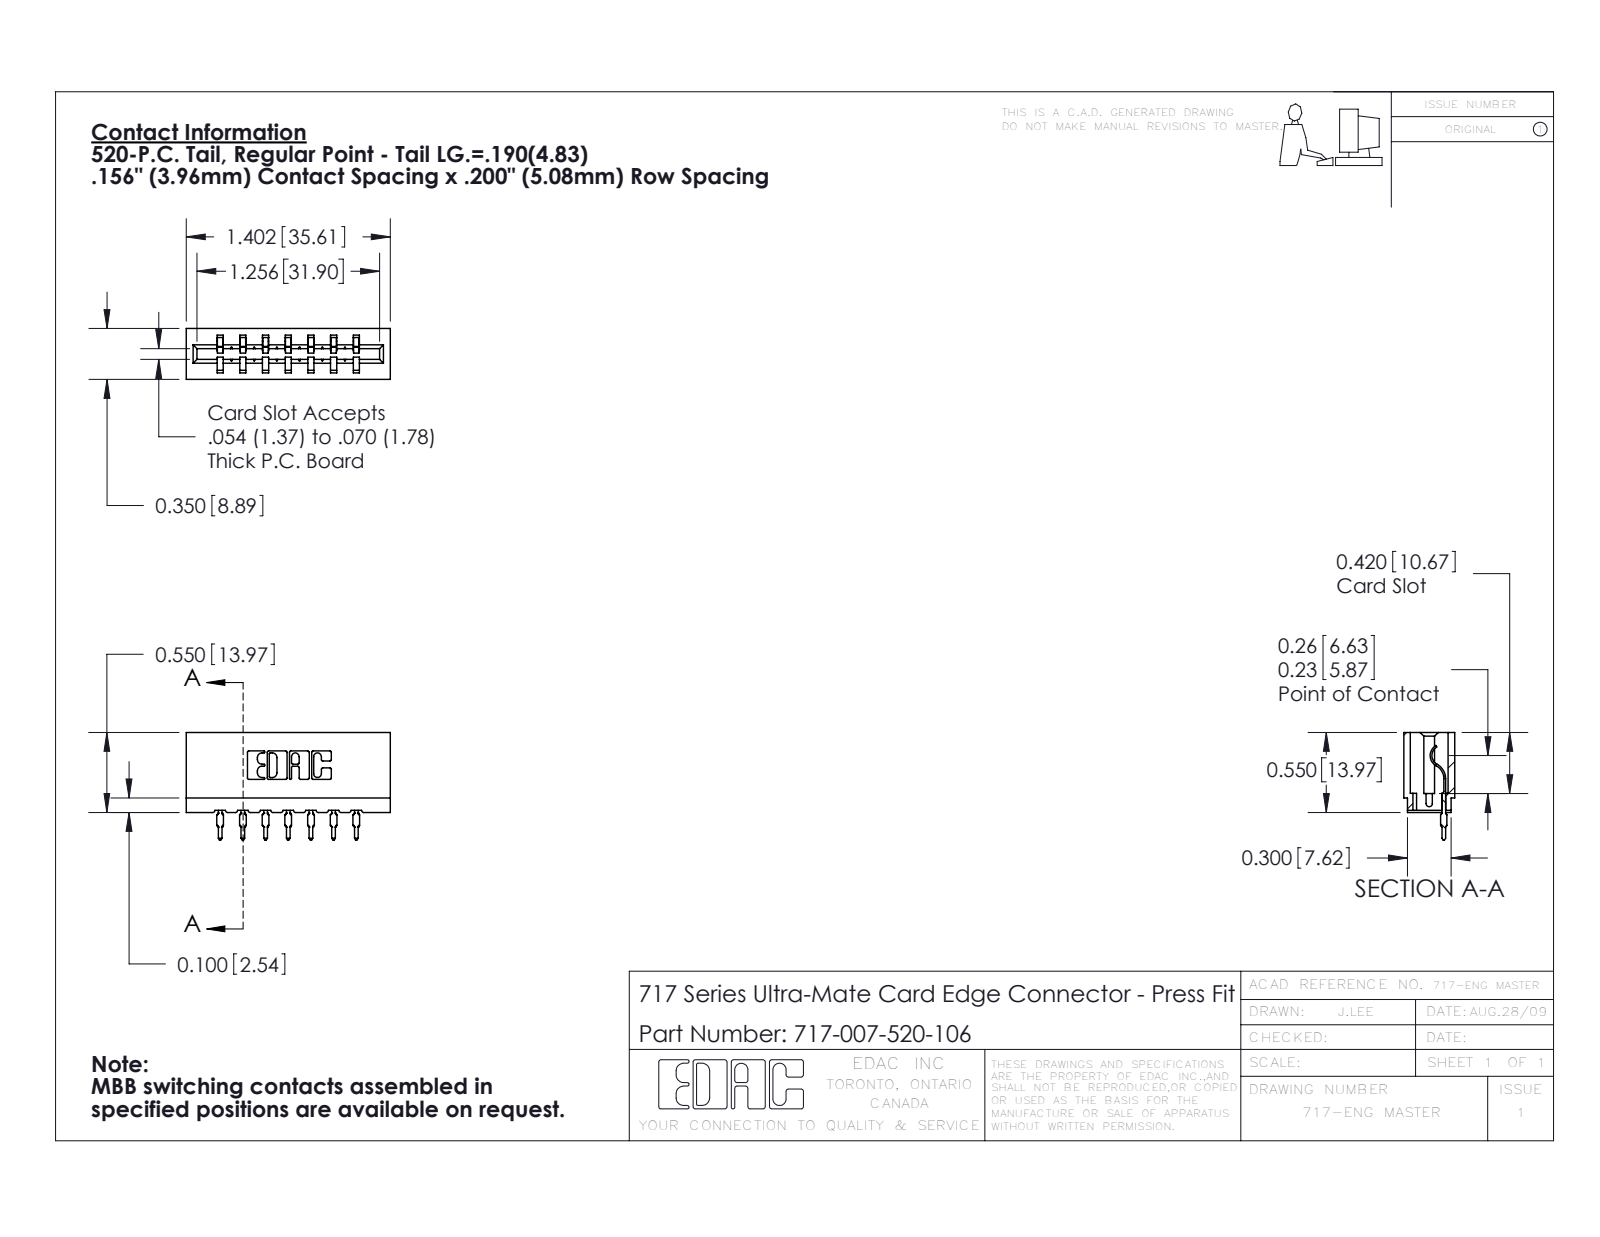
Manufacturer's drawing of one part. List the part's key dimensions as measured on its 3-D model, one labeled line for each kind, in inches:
Part name (STEP PRODUCT): 717-007-520-106; 745-292-001_520; 717 Part_Insulator Option - 06
STEP written by: SolidWorks 2016 (CONFIG_CONTROL_DESIGN)
Units: inches
Bodies: 8 solids, 885 faces (530 planar, 173 cylindrical, 182 other)
Overall size (bounding box): 1.402 × 0.739 × 0.35
Volume: 0.193 in³ · Surface area: 6.205 in²
Partial cylindrical surfaces — rounded edges, fillets, slot ends (radius × count): R0.01 ×22, R0.015 ×14, R0.021 ×14, R0.007 ×6, R0.031 ×6, R0.005 ×4, R0.011 ×4, R0.026 ×3
Main face-to-face distances: 0.212, 0.156, 0.138, 0.35, 0.198, 0.312, 0.468, 0.624, 0.042, 0.27
